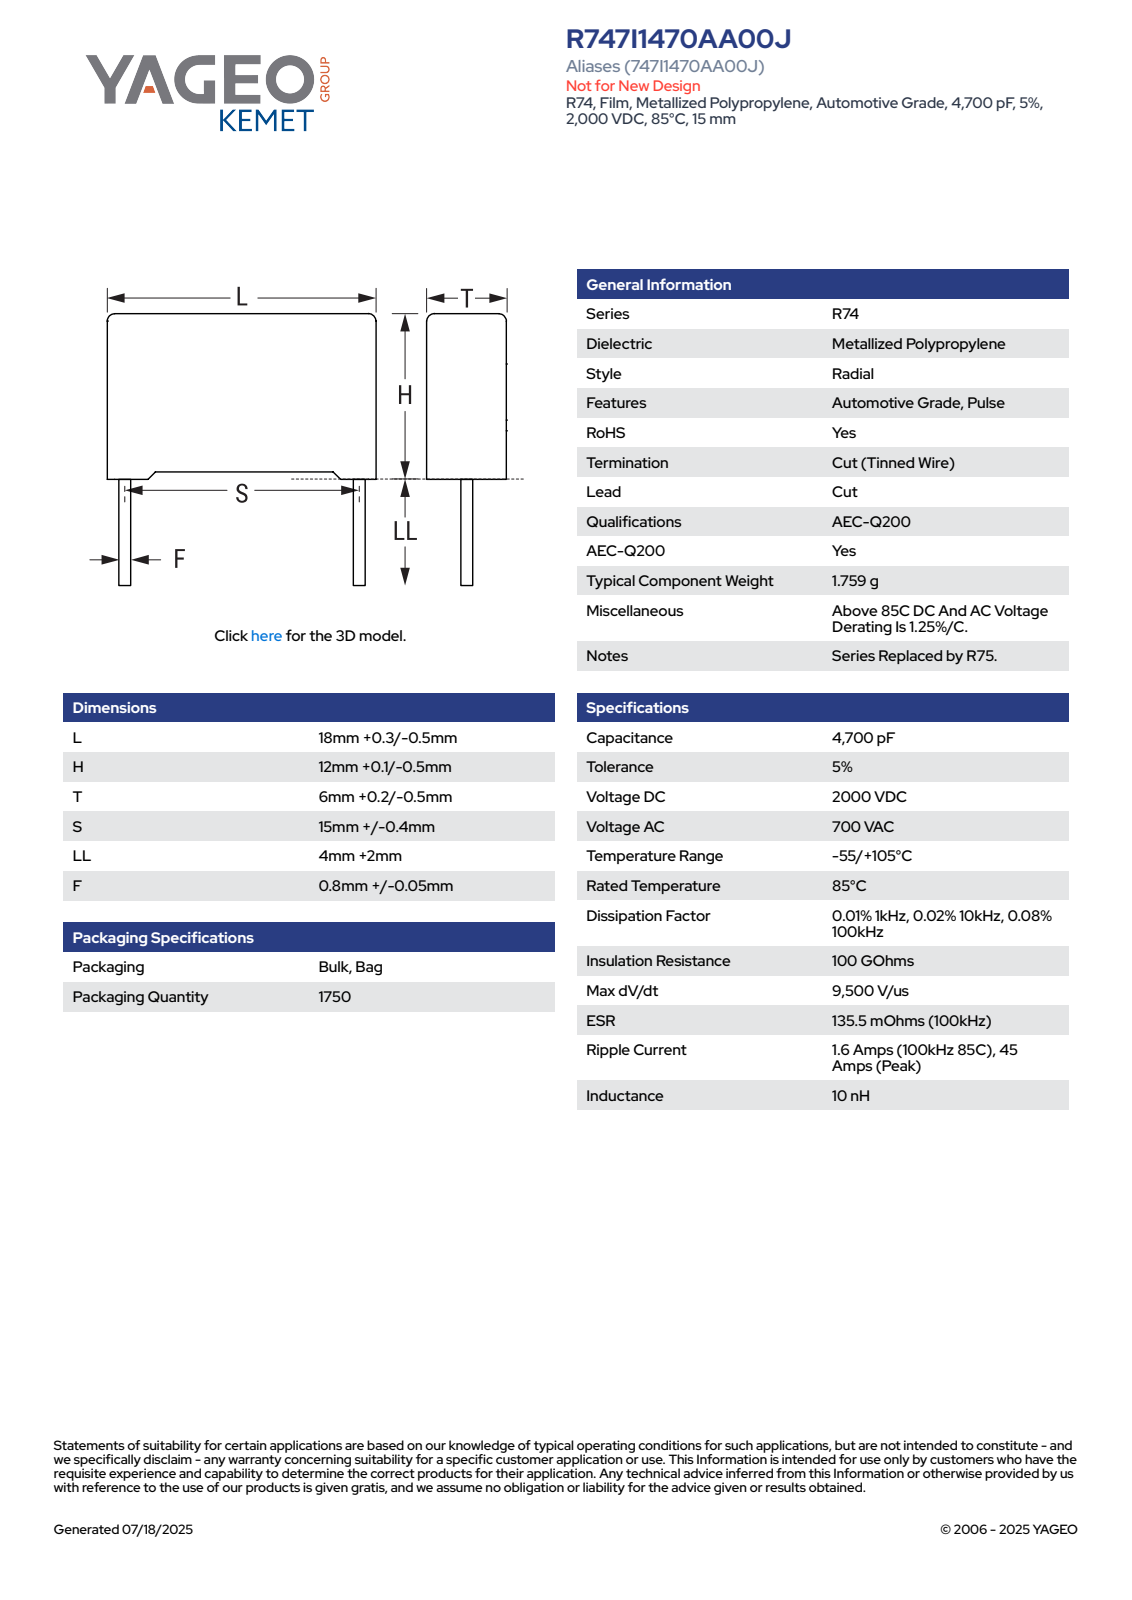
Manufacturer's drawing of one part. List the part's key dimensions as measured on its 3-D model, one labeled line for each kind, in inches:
Part name (STEP PRODUCT): CFR_RB2_18X12X6_L18.3H12.1T6.2S15LL6F0.85
STEP written by: SolidWorks 2021 (AUTOMOTIVE_DESIGN)
Units: inches
Bodies: 4 solids, 85 faces (77 planar, 8 cylindrical, 0 other)
Overall size (bounding box): 0.72 × 0.713 × 0.244
Volume: 0.08 in³ · Surface area: 1.37 in²
Round bosses / shafts (diameter × count): ⌀0.033 ×2
Partial cylindrical surfaces — rounded edges, fillets, slot ends (radius × count): R0.02 ×4
Main face-to-face distances: 0.244, 0.447, 0.72, 0.024, 0.22, 0.03, 0.476, 0.017, 0.013, 0.46
